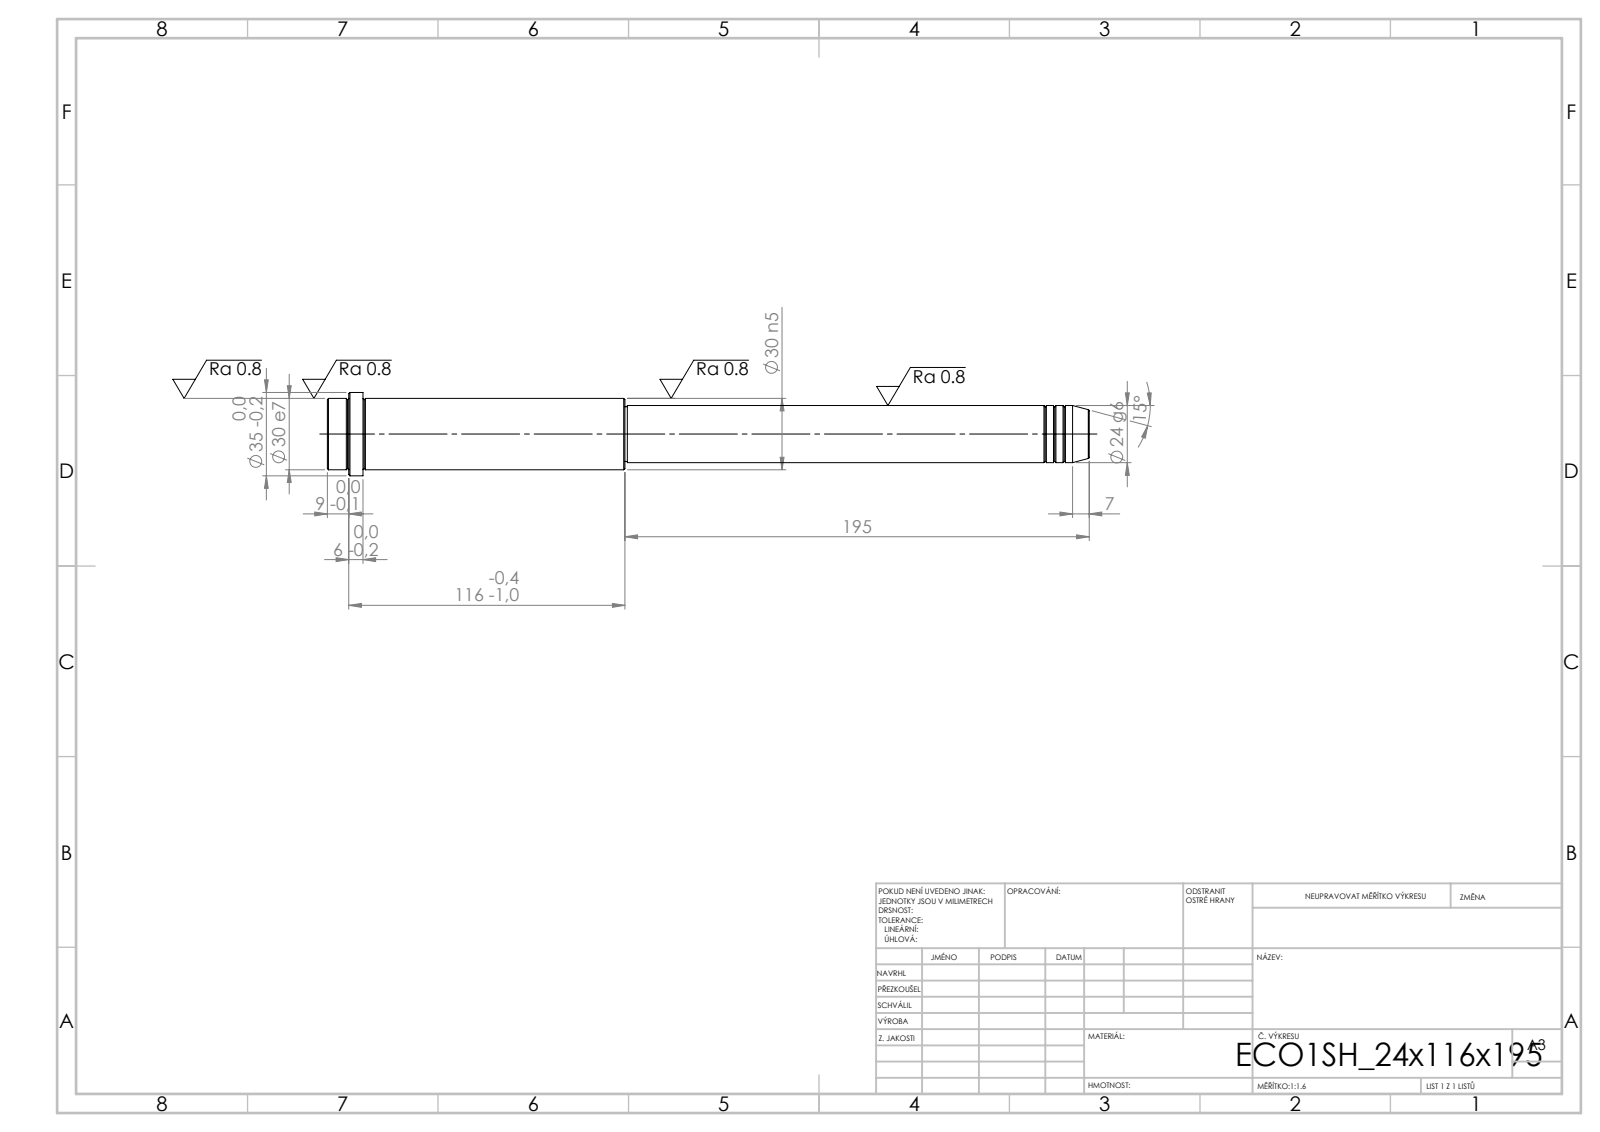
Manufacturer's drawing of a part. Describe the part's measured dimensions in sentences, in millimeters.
Its 3-D file was written by "SolidWorks 2019 (CONFIG_CONTROL_DESIGN)". It is 1 solid with 52 faces: 6 planar, 16 cylindrical and 30 other. Overall it measures 320 by 35 by 35 millimeters. Its volume is 177 400 cubic millimeters and its surface area 28 544 square millimeters. Round bosses or shafts: 1 of diameter 35, 1 of diameter 30, 1 of diameter 24, 1 of diameter 23. The main face-to-face distances are 320, 305, 15, 195, 110, 125, 311, 116, 6, 9.
